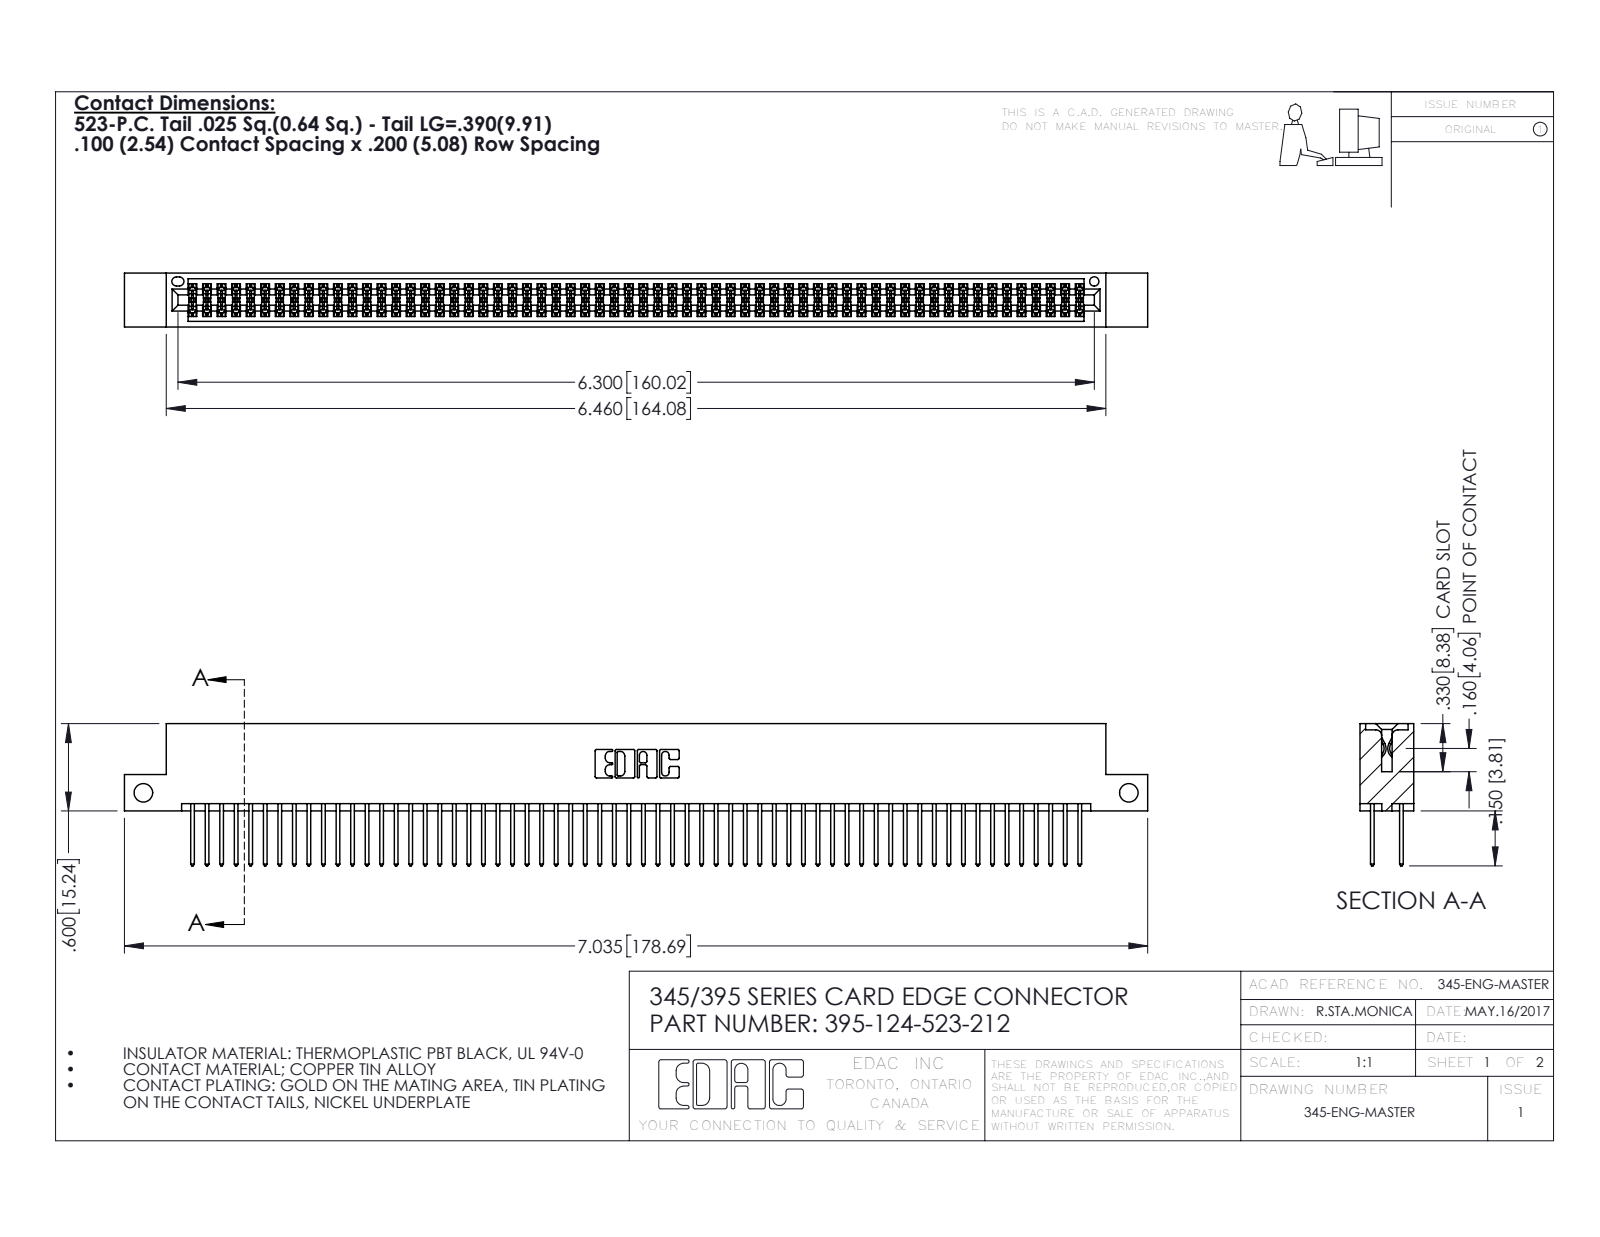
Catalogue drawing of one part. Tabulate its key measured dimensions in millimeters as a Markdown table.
| quantity | value |
| --- | --- |
| part name | 395-124-523-212; 345 Part_Flush Mounting Lugs - Side Mount; 345-292-001_345-293-123 |
| STEP written by | SolidWorks 2016 (CONFIG_CONTROL_DESIGN) |
| units | millimeters |
| bodies | 125 solids, 6326 faces (4172 planar, 2154 cylindrical, 0 other) |
| overall size | 178.7 × 24.8 × 9.4 |
| volume | 17 710 mm³ |
| surface area | 27 570 mm² |
| round holes (diameter × count) | 3.3 × 2, 1.6 × 1 |
| partial cylindrical surfaces (radius × count) | 0.2 × 186, 0.3 × 124, 0.3 × 22, 0.2 × 6, 0.8 × 6, 0.7 × 3, 0.4 × 2, 0.5 × 2 |
| main face-to-face distances | 7.6, 1.8, 5.1, 2.5, 6.9, 0.6, 9.4, 5.7, 4.4, 3.8 |
| hole center spacings | 172.1 |
